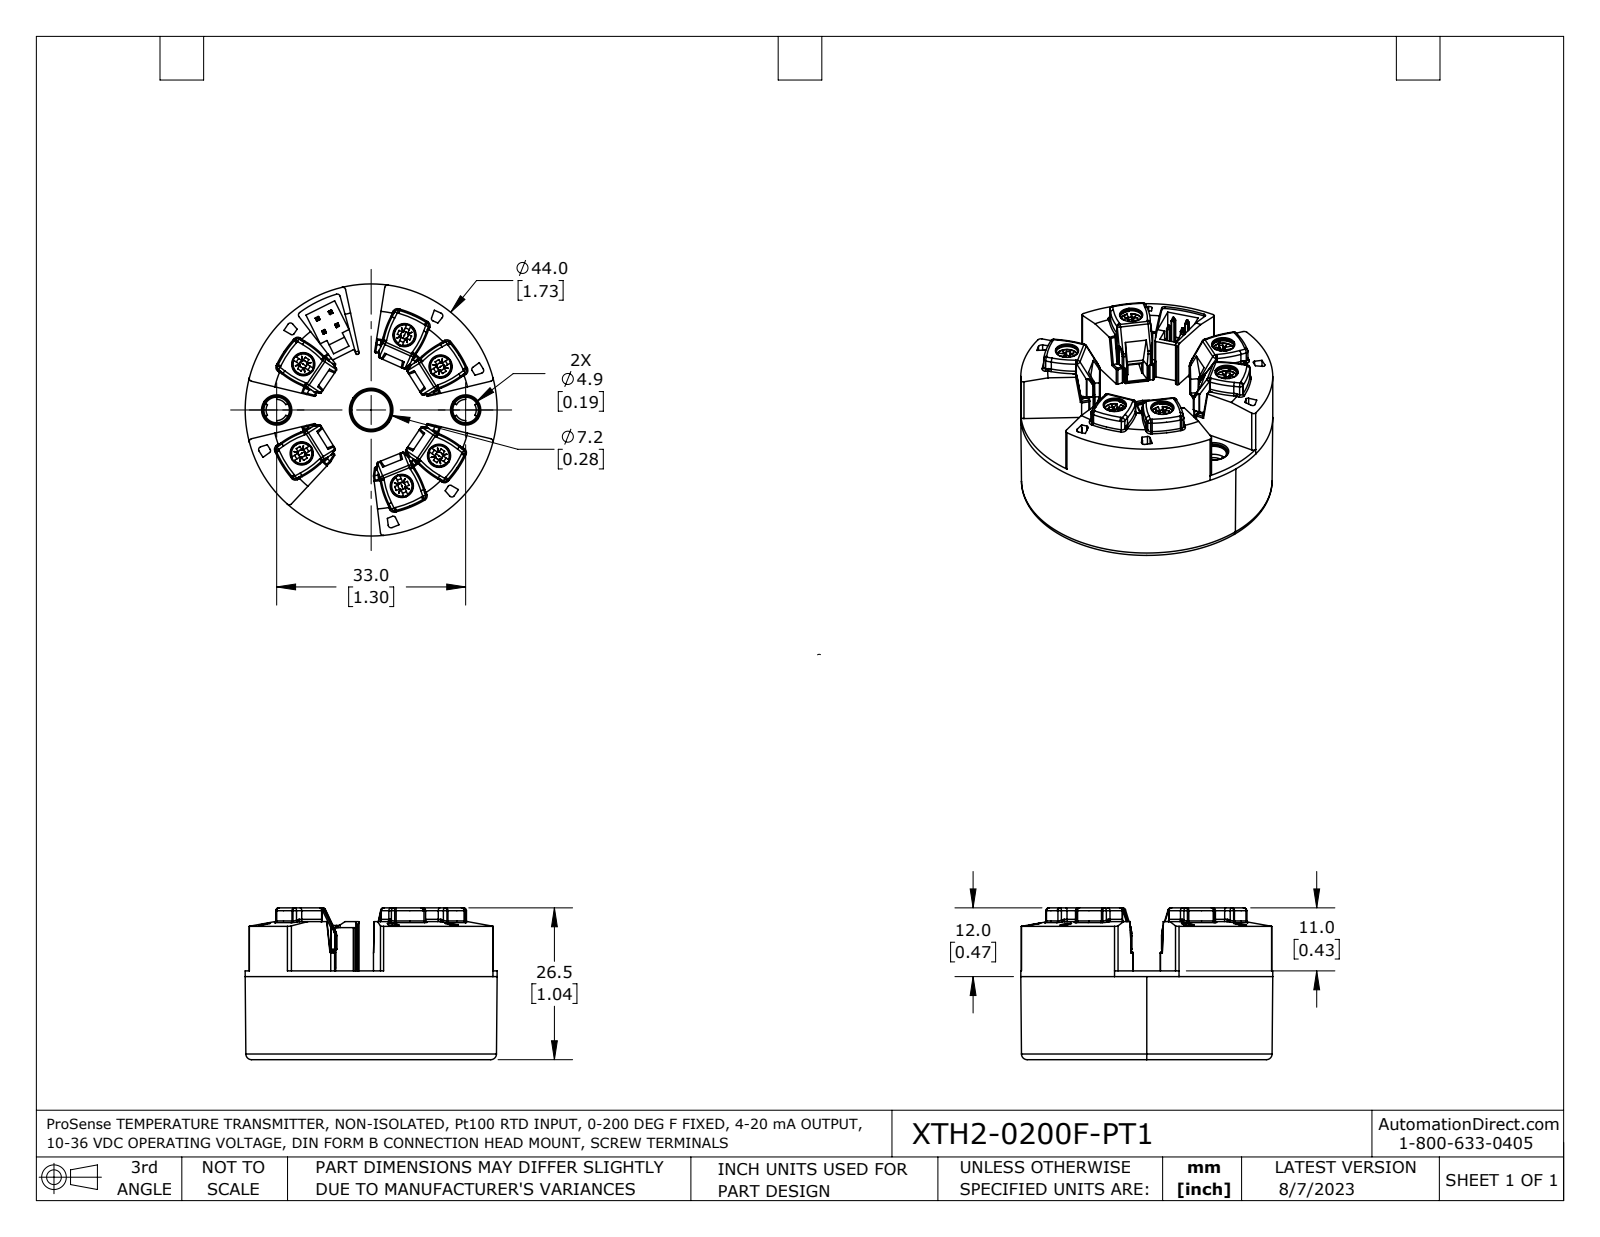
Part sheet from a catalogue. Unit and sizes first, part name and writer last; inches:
Units: inches
Overall size (bounding box): 1.732 × 1.732 × 1.043
Round holes (diameter × count): ⌀0.102 ×6, ⌀0.151 ×6, ⌀0.159 ×6, ⌀0.193 ×2, ⌀0.248 ×2, ⌀0.213 ×1, ⌀0.283 ×1, ⌀0.339 ×1, ⌀0.685 ×1
Round bosses / shafts (diameter × count): ⌀0.106 ×12, ⌀0.156 ×6, ⌀0.098 ×6, ⌀1.732 ×1, ⌀1.646 ×1, ⌀0.402 ×1
Partial cylindrical surfaces — rounded edges, fillets, slot ends (radius × count): R0.008 ×247, R0.02 ×144, R0.012 ×58, R0.004 ×48, R0.01 ×36, R0.006 ×18, R0.016 ×12, R0.592 ×12
Main face-to-face distances: 0.039, 0.571, 0.453, 0.118, 0.492, 0.61, 0.079, 0.531, 0.098, 0.067
Hole centre spacings: 0.563, 0.863, 0.329, 0.344, 0.364, 0.563, 0.613, 0.65
Volume: 0.846 in³ · Surface area: 24.66 in²
Bodies: 1 solid, 2500 faces (944 planar, 967 cylindrical, 589 other)
Part name (STEP PRODUCT): XTH2-0200F-PT1
STEP written by: SolidWorks 2021 (AUTOMOTIVE_DESIGN)
